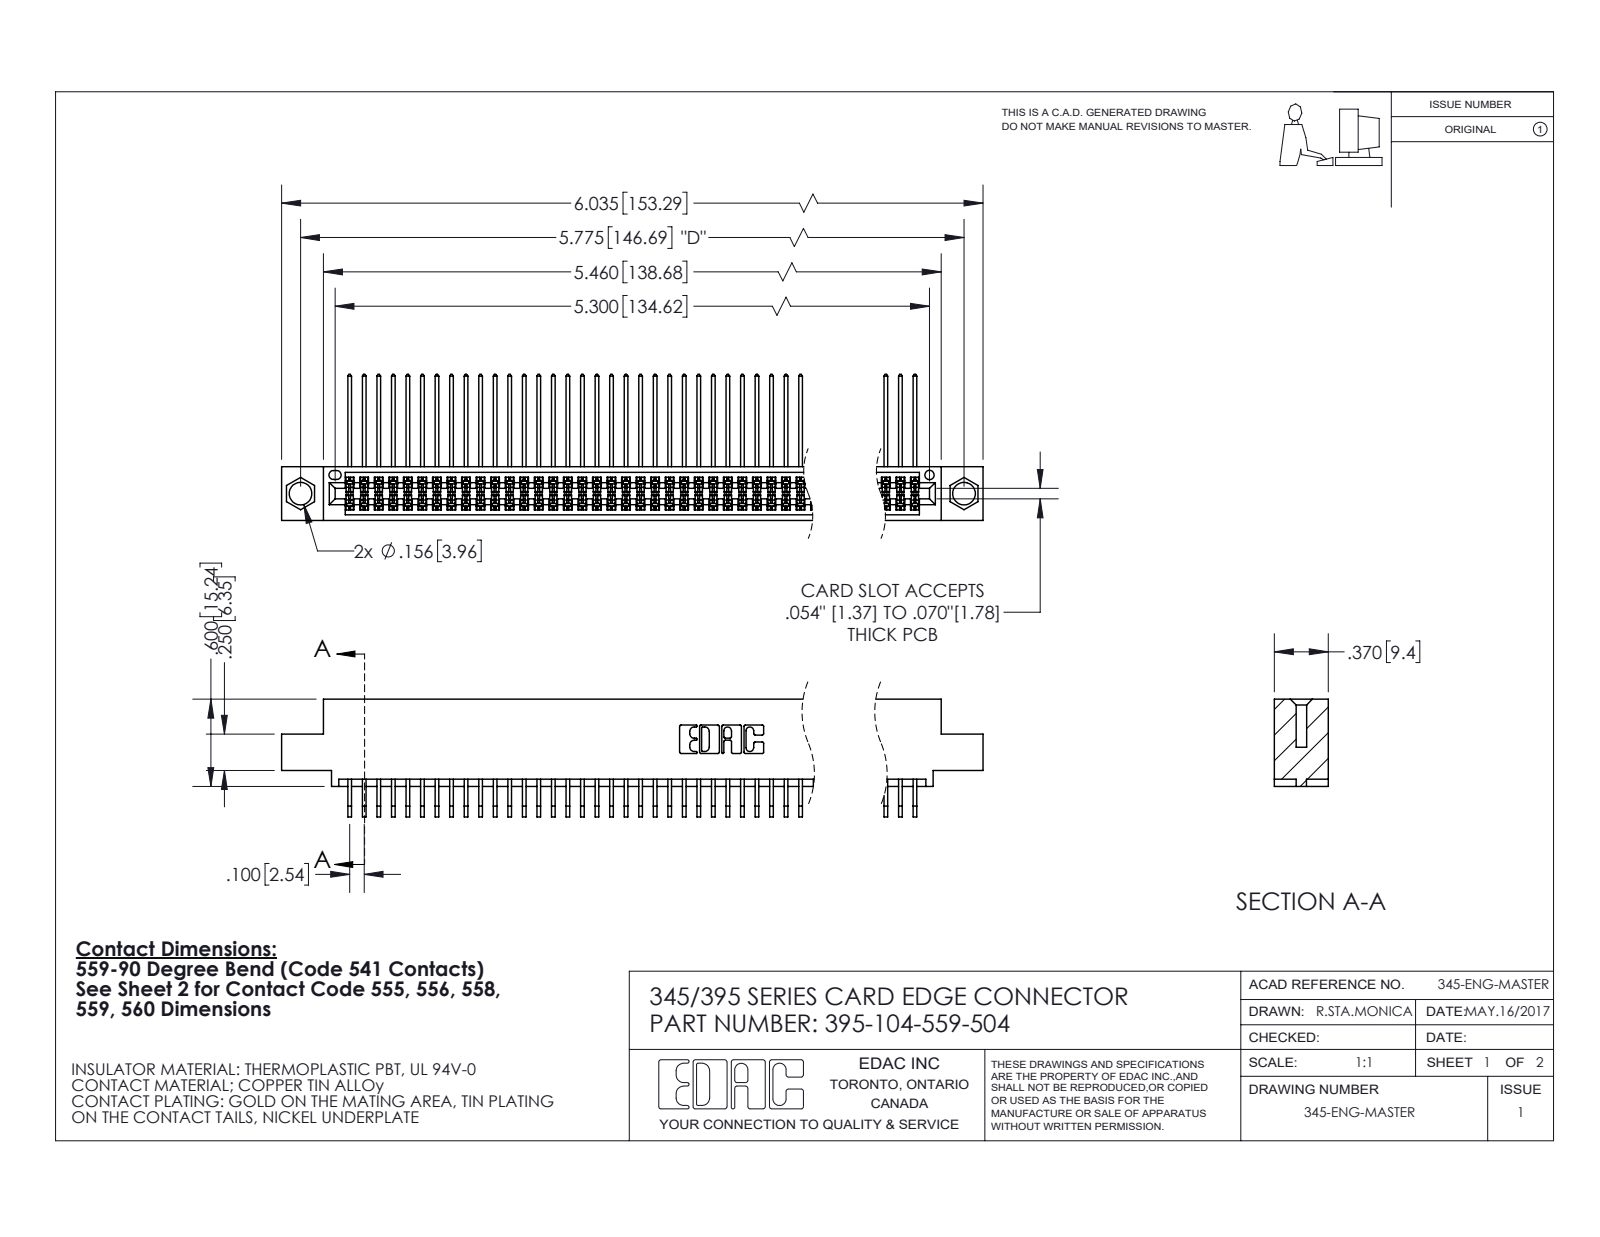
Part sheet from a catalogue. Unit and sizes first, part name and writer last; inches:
Units: inches
Overall size (bounding box): 6.035 × 1.005 × 0.809
Round holes (diameter × count): ⌀0.156 ×2, ⌀0.064 ×1
Partial cylindrical surfaces — rounded edges, fillets, slot ends (radius × count): R0.006 ×208, R0.01 ×22, R0.007 ×6, R0.031 ×6, R0.026 ×3, R0.014 ×2, R0.019 ×2, R0.022 ×2
Main face-to-face distances: 0.072, 0.298, 0.2, 0.37, 0.098, 0.272, 0.025, 0.225, 0.175, 0.15
Hole centre spacings: 0.27, 5.539, 5.775
Volume: 0.94 in³ · Surface area: 39.88 in²
Bodies: 105 solids, 5552 faces (3738 planar, 1814 cylindrical, 0 other)
Part name (STEP PRODUCT): 345-292-001_558 559 Tail - 1; 345 Part_0.110 Offset - 0.156 Dia-TI; 345-292-001_559 Tail - 2; 395-104-559-504
STEP written by: SolidWorks 2020 (CONFIG_CONTROL_DESIGN)
